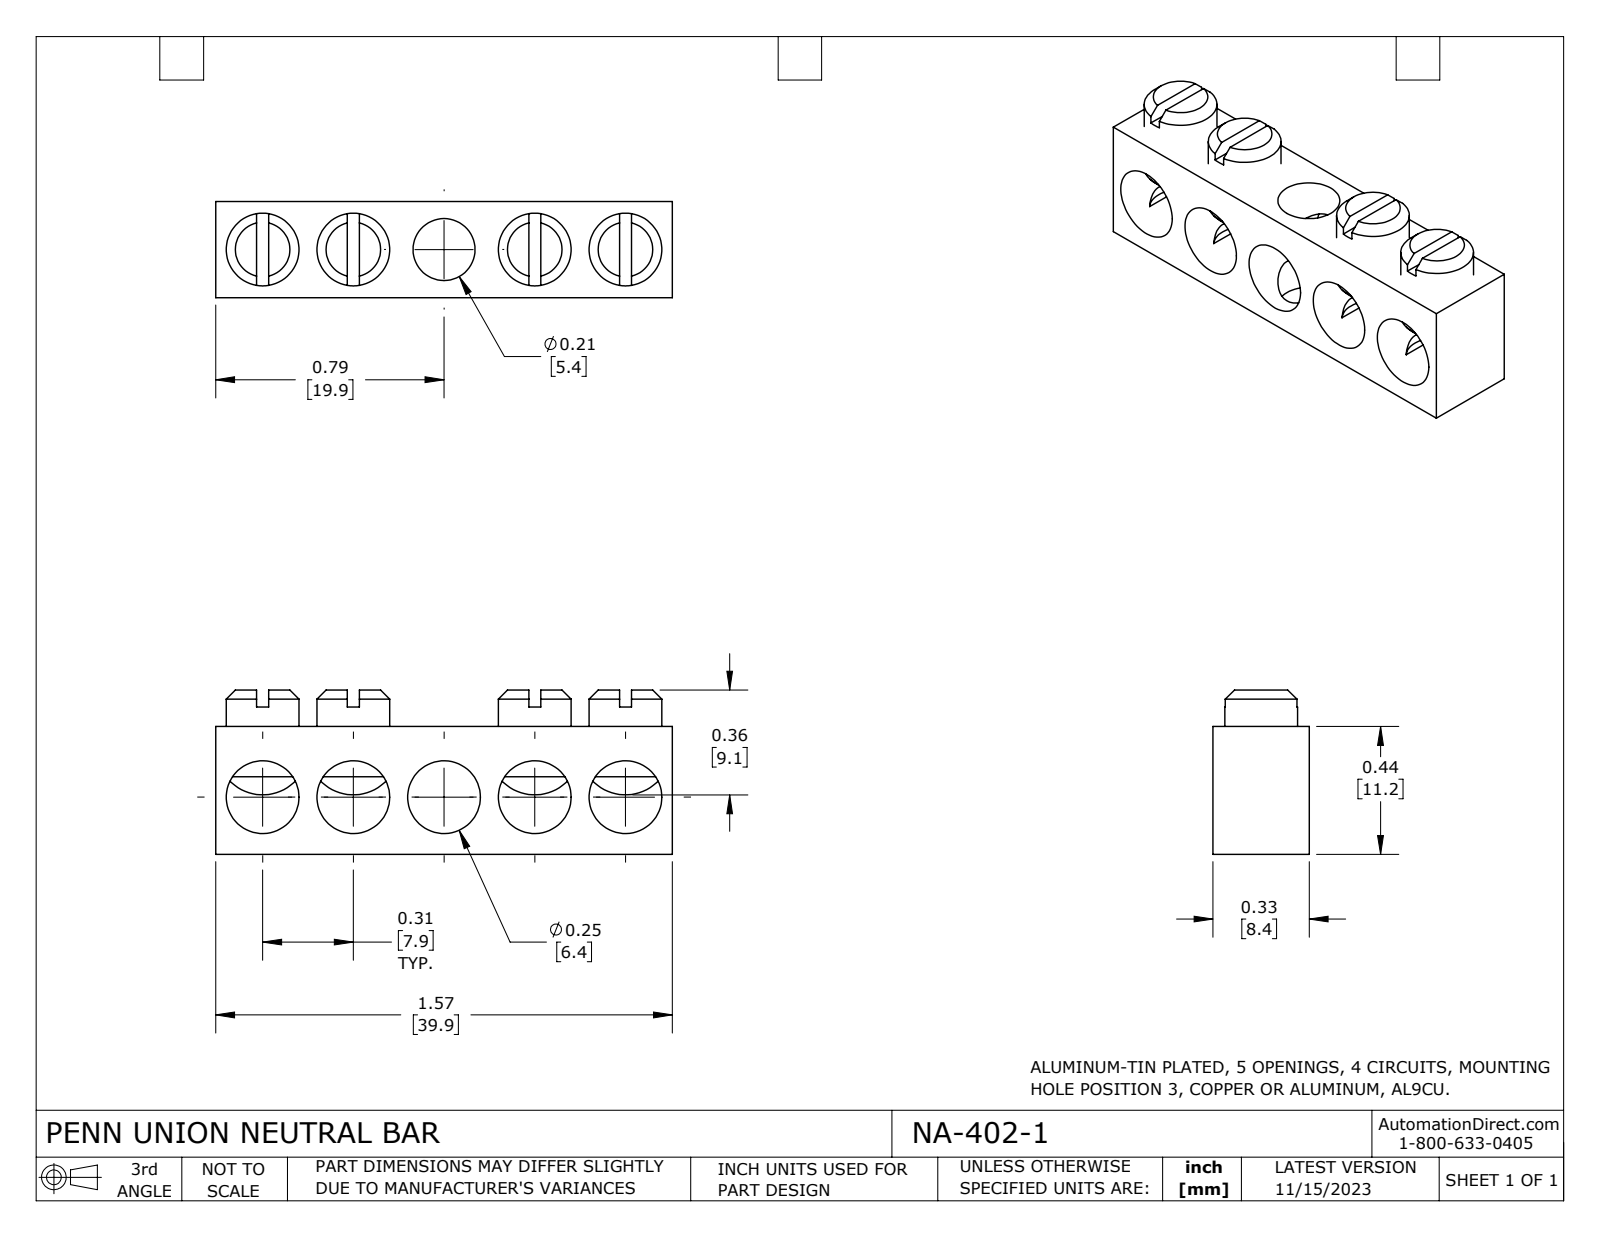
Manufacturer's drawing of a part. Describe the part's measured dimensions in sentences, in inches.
The part is named "NA-402-1". Its 3-D file was written by "SolidWorks 2023 (CONFIG_CONTROL_DESIGN)". It is 5 solids with 92 faces: 34 planar, 38 cylindrical and 20 other. Overall it measures 1.57 by 0.565 by 0.331 inches. Its volume is 0.182 cubic inches and its surface area 5.037 square inches. Round holes: 5 of diameter 0.213, 5 of diameter 0.25. Round bosses or shafts: 4 of diameter 0.25. The main face-to-face distances are 0.331, 0.44, 1.57, 0.565, 0.125, 0.312, 0.935, 0.041, 0.507, 0.067. The hole center spacings are 0.312, 0.624, 0.935, 1.247.
